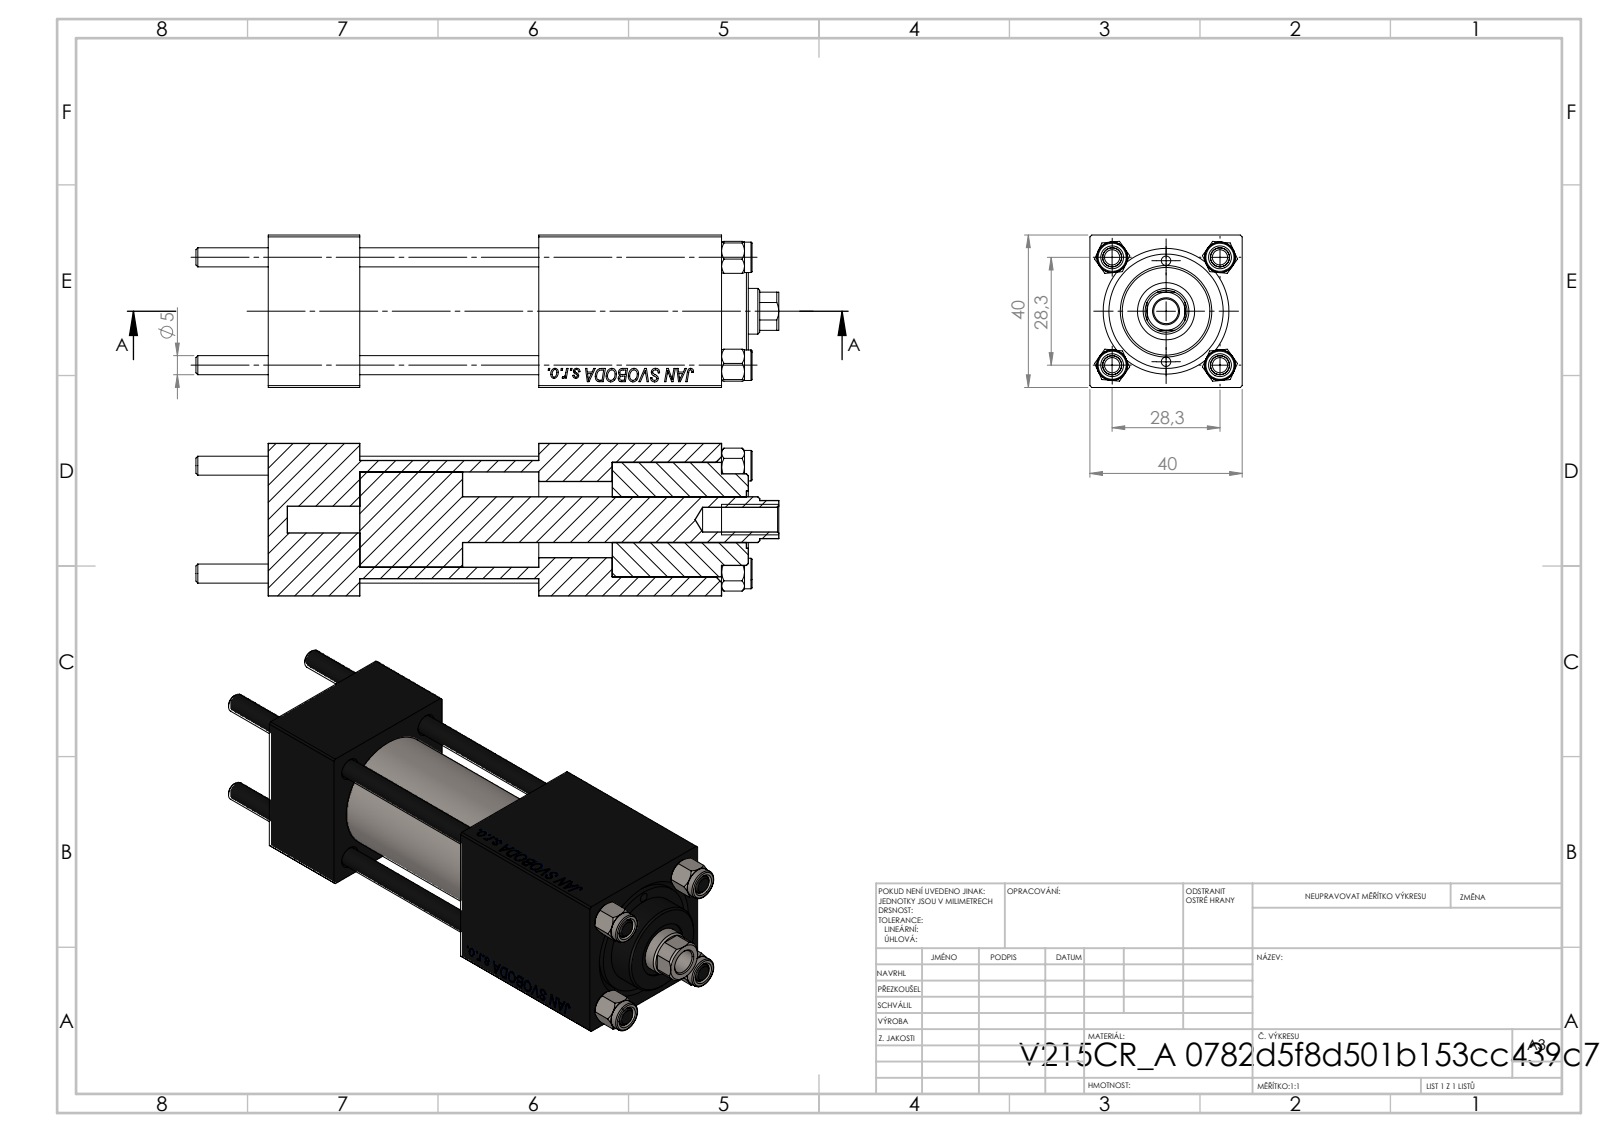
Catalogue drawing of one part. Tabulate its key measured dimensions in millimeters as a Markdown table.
| quantity | value |
| --- | --- |
| part name | V215CR_BODY_A; NUT_M5; CR025_012_A_0_G_A_G_M_020_+#_##_TYCINKA; V215_VC_A (+1 more) |
| STEP written by | SolidWorks 2019 (CONFIG_CONTROL_DESIGN) |
| units | millimeters |
| bodies | 11 solids, 1137 faces (519 planar, 82 cylindrical, 536 other) |
| overall size | 153 × 40 × 40 |
| volume | 144 775 mm³ |
| surface area | 58 950 mm² |
| round holes (diameter × count) | 5 × 4, 20 × 3, 2.5 × 2, 7 × 2, 13.16 × 2, 6.5 × 1, 12 × 1, 15 × 1, 25 × 1, 30 × 1 |
| round bosses / shafts (diameter × count) | 8 × 4, 31 × 1, 24 × 1 |
| partial cylindrical surfaces (radius × count) | 5.5 × 1 |
| main face-to-face distances | 40, 24, 90.3, 66.3, 119, 95, 28.7, 71, 47, 19.3 |
| hole center spacings | 14.18, 20.01, 28.3, 30.84, 13.25, 40.02, 26.5, 72 |
